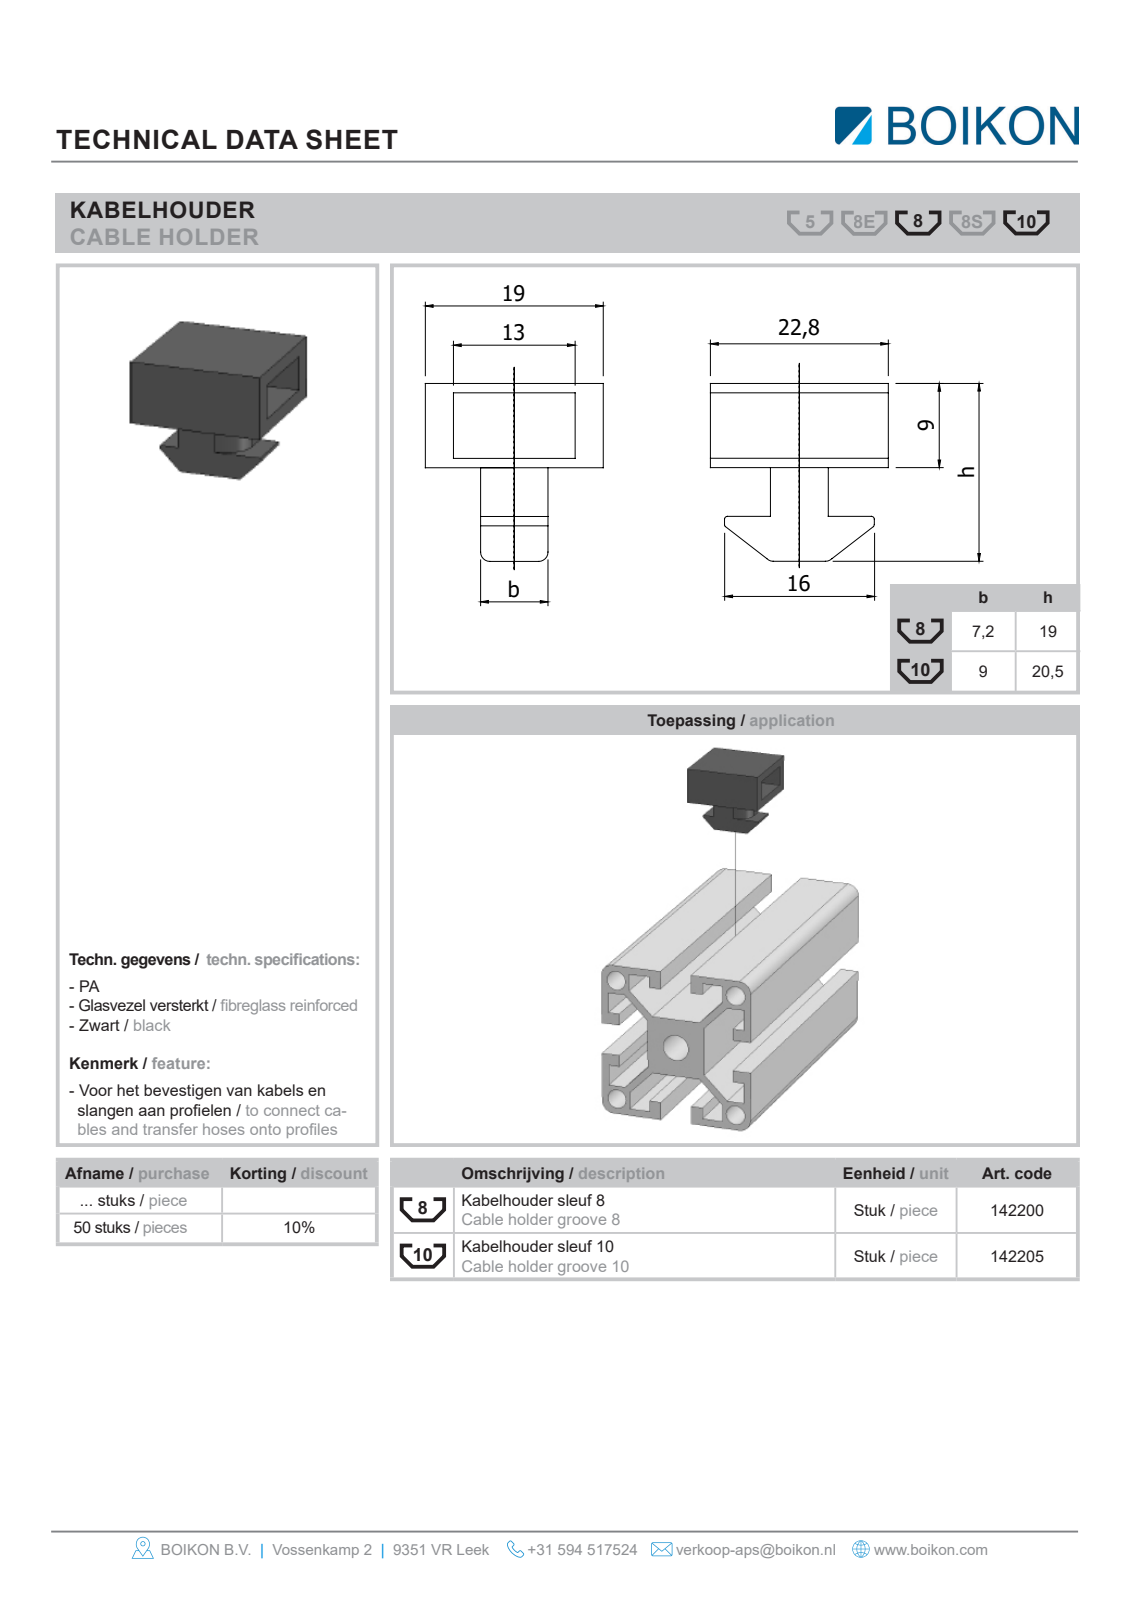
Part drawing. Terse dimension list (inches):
name: Root; 142200Kabelhouder sleuf 8BOIKON
written by: HiCAD 2013 1802.4 Build 509 (AUTOMOTIVE_DESIGN)
unit: in
bodies: 1 solid, 23 faces (21 planar, 2 cylindrical, 0 other)
size: 0.748 × 0.748 × 0.689
volume: 0.161 in³; area: 3.591 in²
rounds: 2× R0.157
face distances: 0.276, 0.079, 0.354, 0.197, 0.748, 0.118, 0.63, 0.23, 0.518, 0.112
